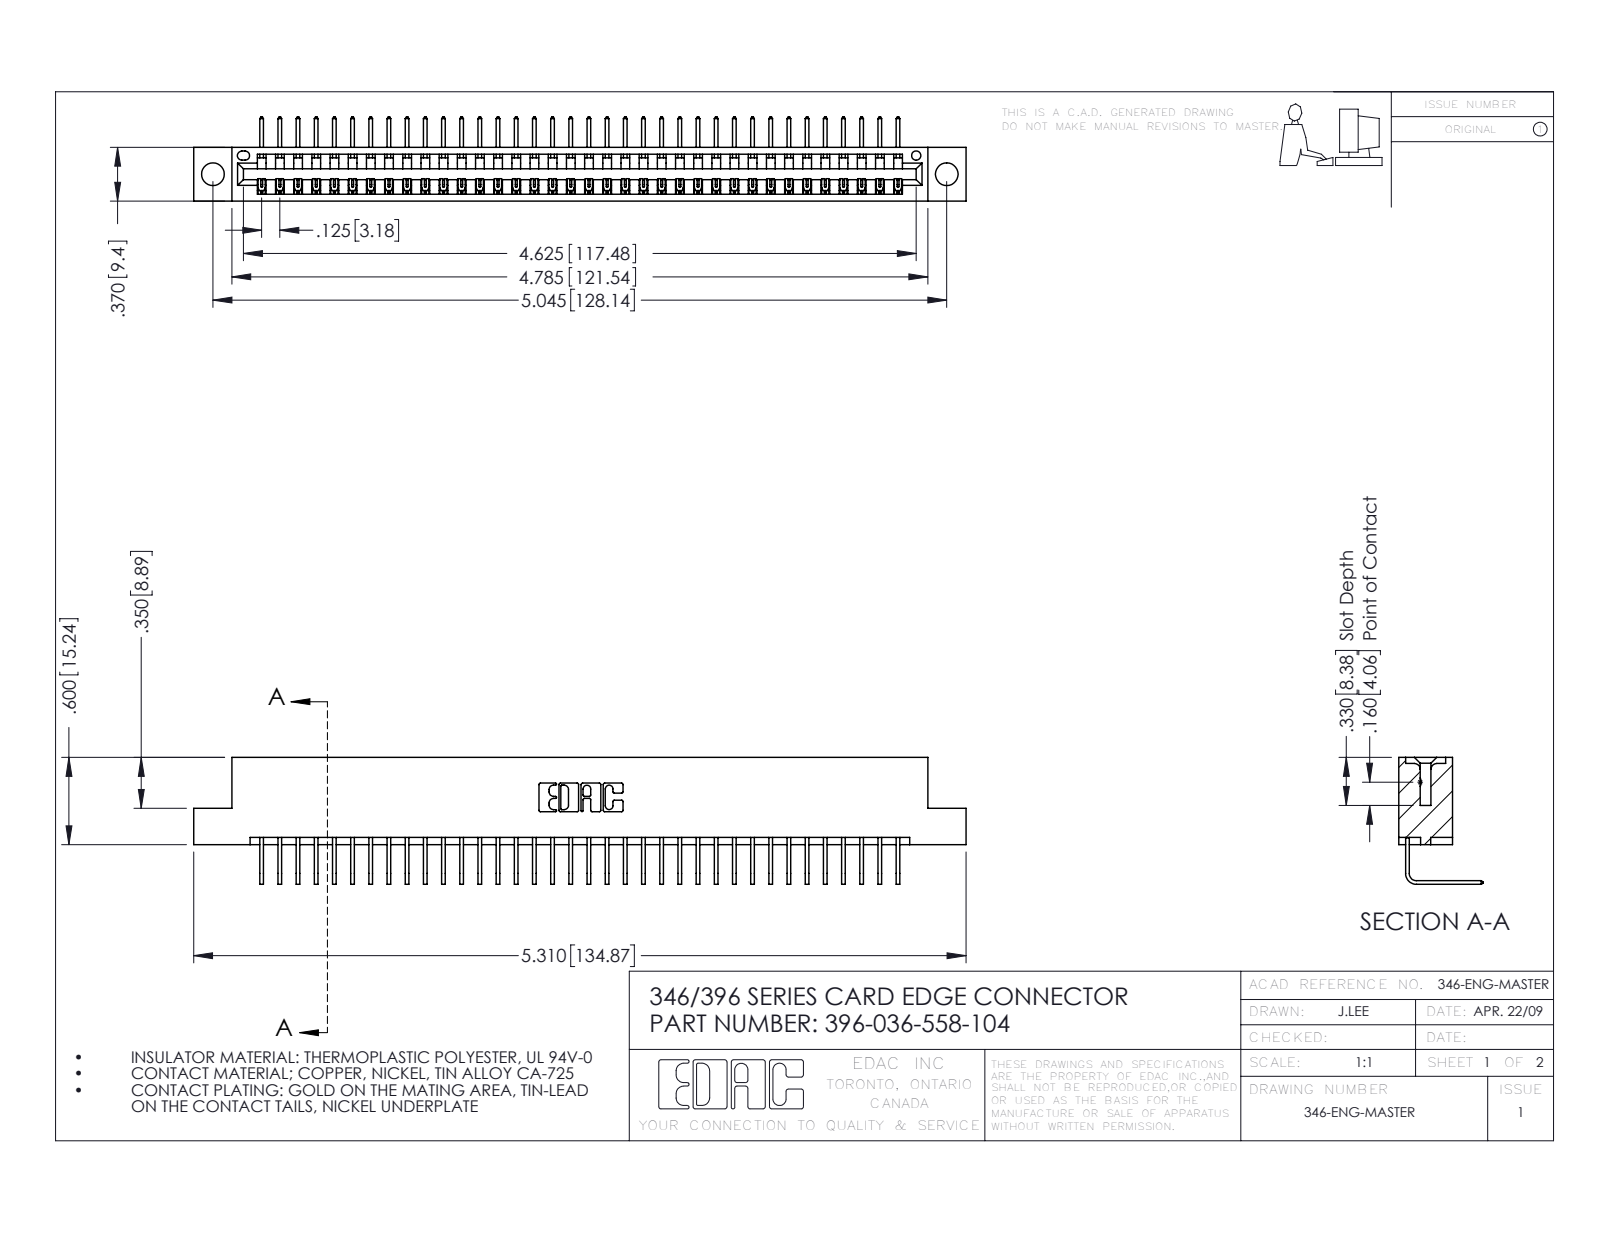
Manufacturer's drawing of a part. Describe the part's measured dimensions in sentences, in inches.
The part is named "396-036-558-104; 345-292-001_558 Tail - 2; 346 Part_Flush Mounting Lugs - 0.156 Dia-TH". Its 3-D file was written by "SolidWorks 2016 (CONFIG_CONTROL_DESIGN)". It is 37 solids with 2282 faces: 1588 planar, 694 cylindrical and 0 other. Overall it measures 5.31 by 0.873 by 0.58 inches. Its volume is 0.787 cubic inches and its surface area 25.7 square inches. Round holes: 2 of diameter 0.156, 1 of diameter 0.064. Partial cylindrical surfaces (rounded edges, fillets, slot ends): 72 of radius 0.006, 22 of radius 0.01, 6 of radius 0.007, 6 of radius 0.031, 3 of radius 0.026, 2 of radius 0.031, 2 of radius 0.04, 1 of radius 0.014. The main face-to-face distances are 0.322, 0.048, 0.37, 0.25, 0.298, 0.025, 0.072, 0.148, 0.222, 0.1. The hole center spacings are 0.246, 4.836, 5.045.
